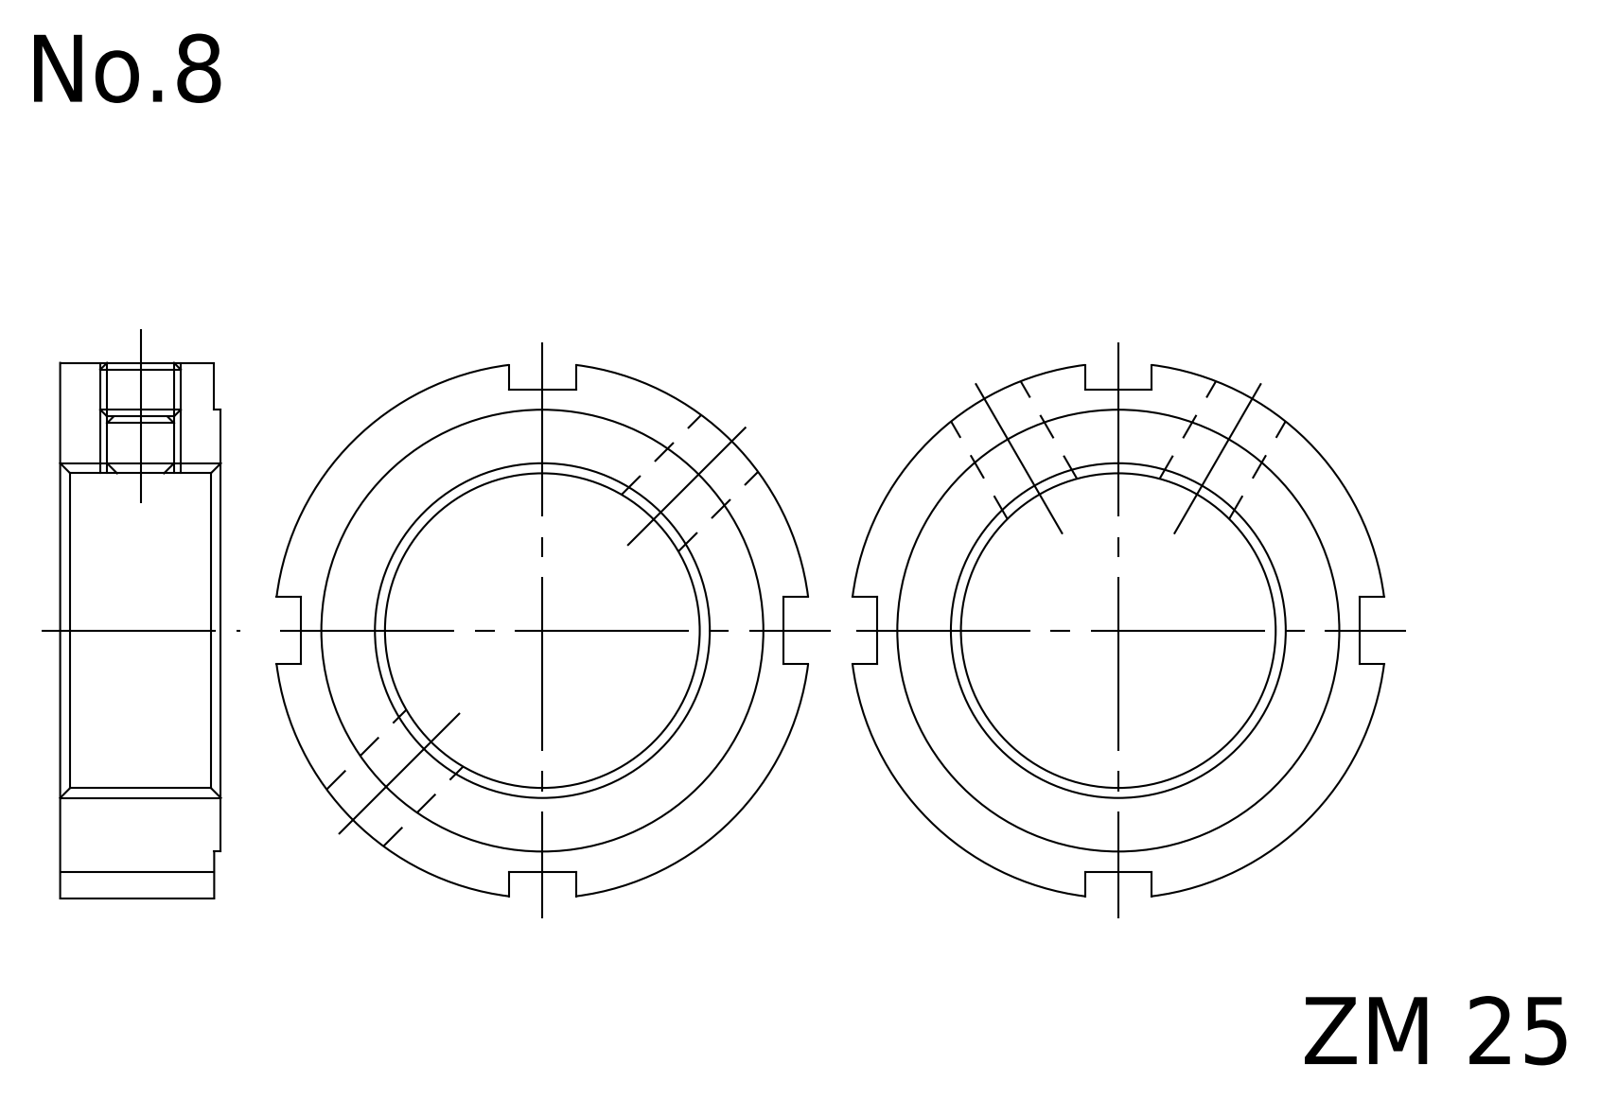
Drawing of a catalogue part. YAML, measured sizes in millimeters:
part_name: "FKD ZM 25A"
step_written_by: "Autodesk Inventor 2011 (AUTOMOTIVE_DESIGN)"
units: millimeters
bodies: {solids: 1, faces: 23, planar: 15, cylindrical: 8, other: 0}
overall_size: [39.69, 39.69, 12]
volume: 8255
surface_area: 4219
round_holes:
  - {diameter: 4.92, count: 2}
  - {diameter: 25, count: 1}
round_bosses_or_shafts:
  - {diameter: 40, count: 1}
  - {diameter: 33, count: 1}
face_to_face_distances: [12, 0.5, 11.5, 15.5, 20.5, 36, 5]
